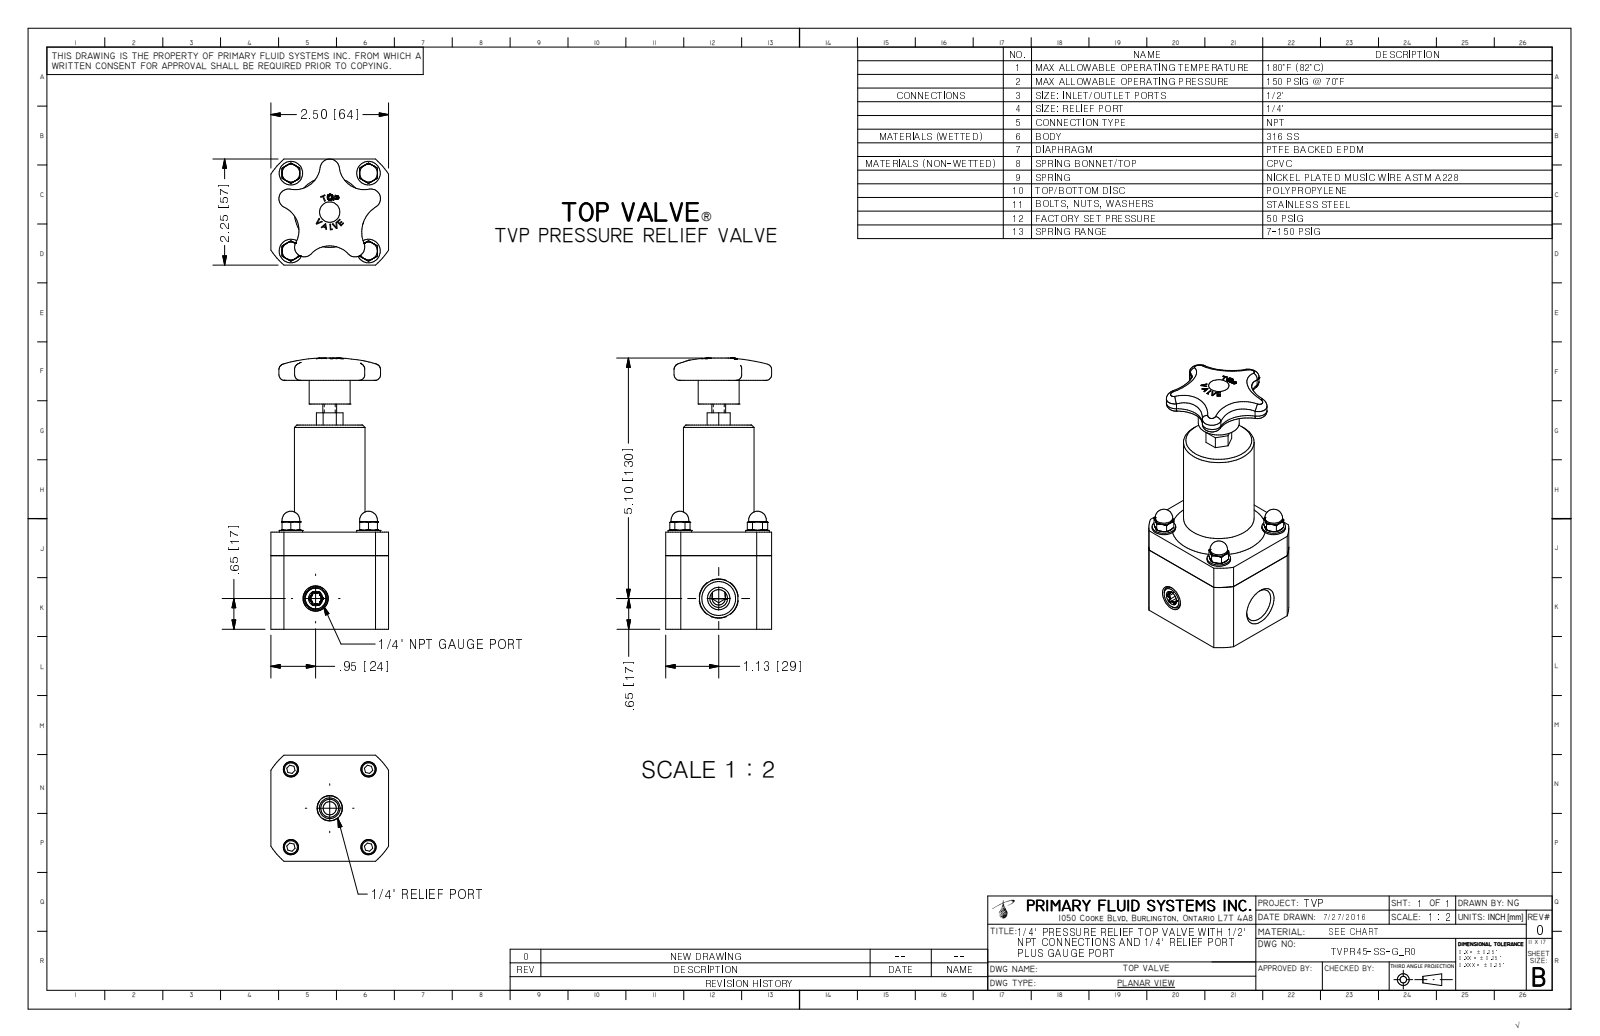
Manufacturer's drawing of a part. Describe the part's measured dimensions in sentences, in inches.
The part is named "TVPR45-SS-G_R0". Its 3-D file was written by "Autodesk Inventor 2009 (AUTOMOTIVE_DESIGN)". It is 1 solid with 378 faces: 155 planar, 54 cylindrical and 169 other. Overall it measures 5.75 by 2.5 by 2.25 inches. Its volume is 16.09 cubic inches and its surface area 57.61 square inches. Round holes: 4 of diameter 0.147, 1 of diameter 0.437, 1 of diameter 0.719, 1 of diameter 1.525. Round bosses or shafts: 4 of diameter 0.5, 4 of diameter 0.375, 4 of diameter 0.312, 1 of diameter 1.5, 1 of diameter 0.87, 1 of diameter 0.293. Partial cylindrical surfaces (rounded edges, fillets, slot ends): 6 of radius 0.027, 5 of radius 0.085, 5 of radius 0.205, 4 of radius 0.536, 4 of radius 0.656, 1 of radius 0.625, 1 of radius 0.745, 1 of radius 1.488. The main face-to-face distances are 2.25, 2.5, 2.06, 4.33, 2.27, 0.6, 1.9, 4.776, 2.716, 0.446. The hole center spacings are 1.167, 1.167, 1.65, 1.65, 2.334.
